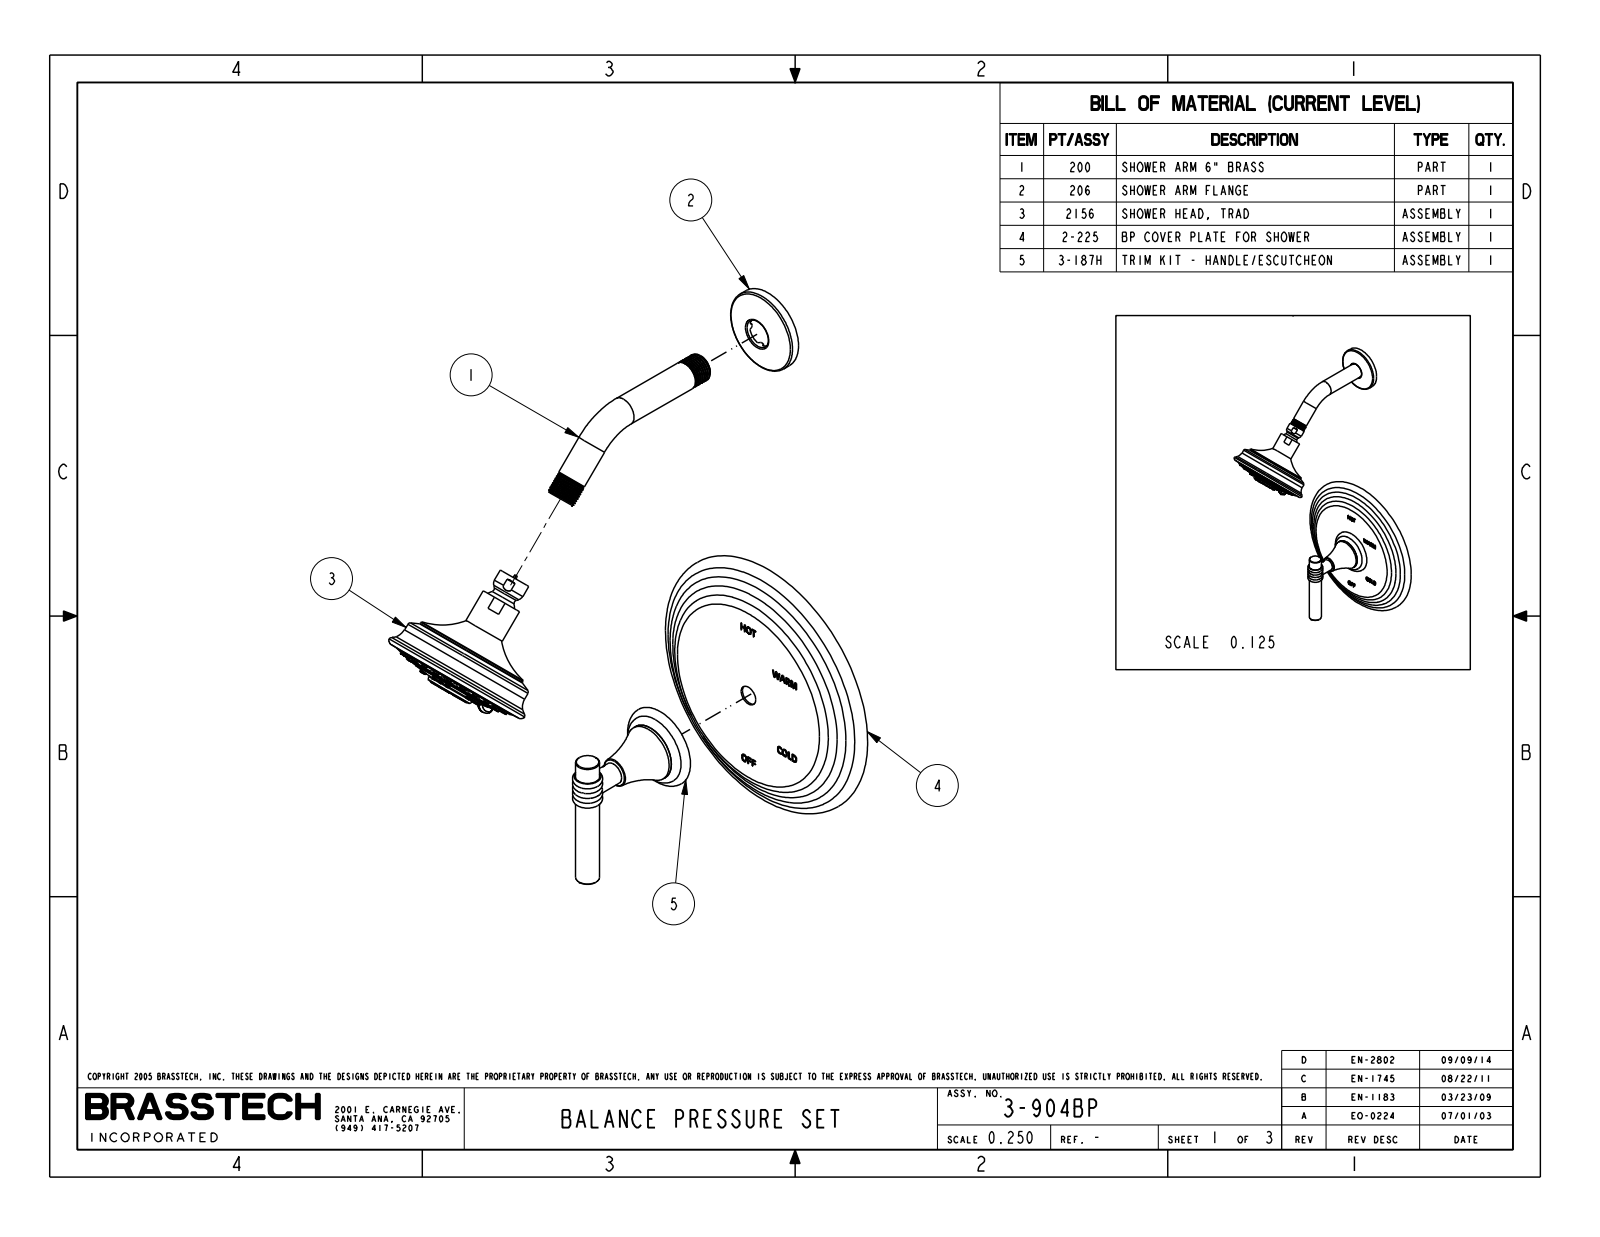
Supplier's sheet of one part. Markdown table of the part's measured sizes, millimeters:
| quantity | value |
| --- | --- |
| part name | 10106_AF0; H-78; 2-225_ASM; 10050 (+8 more) |
| STEP written by | PRO/ENGINEER BY PARAMETRIC TECHNOLOGY CORPORATION, 2013150 (CONFIG_CONTROL_DESIGN) |
| units | millimeters |
| bodies | 51 solids, 7317 faces (3258 planar, 1682 cylindrical, 2377 other) |
| overall size | 433.5 × 229.1 × 196.9 |
| volume | 258 800 mm³ |
| surface area | 399 000 mm² |
| round holes (diameter × count) | 1.1 × 32, 2.5 × 15, 1.5 × 12, 2 × 8, 2.4 × 8, 4.7 × 8, 3 × 7, 3.8 × 3, 6.4 × 3, 7 × 3, 3.3 × 2, 6.8 × 2 |
| round bosses / shafts (diameter × count) | 3.6 × 39, 4.2 × 23, 8 × 3, 6.2 × 3, 59 × 2, 20.7 × 2, 19.5 × 2, 8.2 × 2 |
| partial cylindrical surfaces (radius × count) | 0.5 × 53, 0.3 × 29, 2.1 × 15, 0.2 × 14, 2 × 9, 0.8 × 8, 2.2 × 8, 18.9 × 5 |
| main face-to-face distances | 1.3, 2.5, 5.3, 7.8, 4.8, 7.3, 2.7, 2.6, 0.5, 2 |
| hole center spacings | 9.6, 7, 10.7, 6.1, 17.7, 9.8, 10.7, 15.6 |
